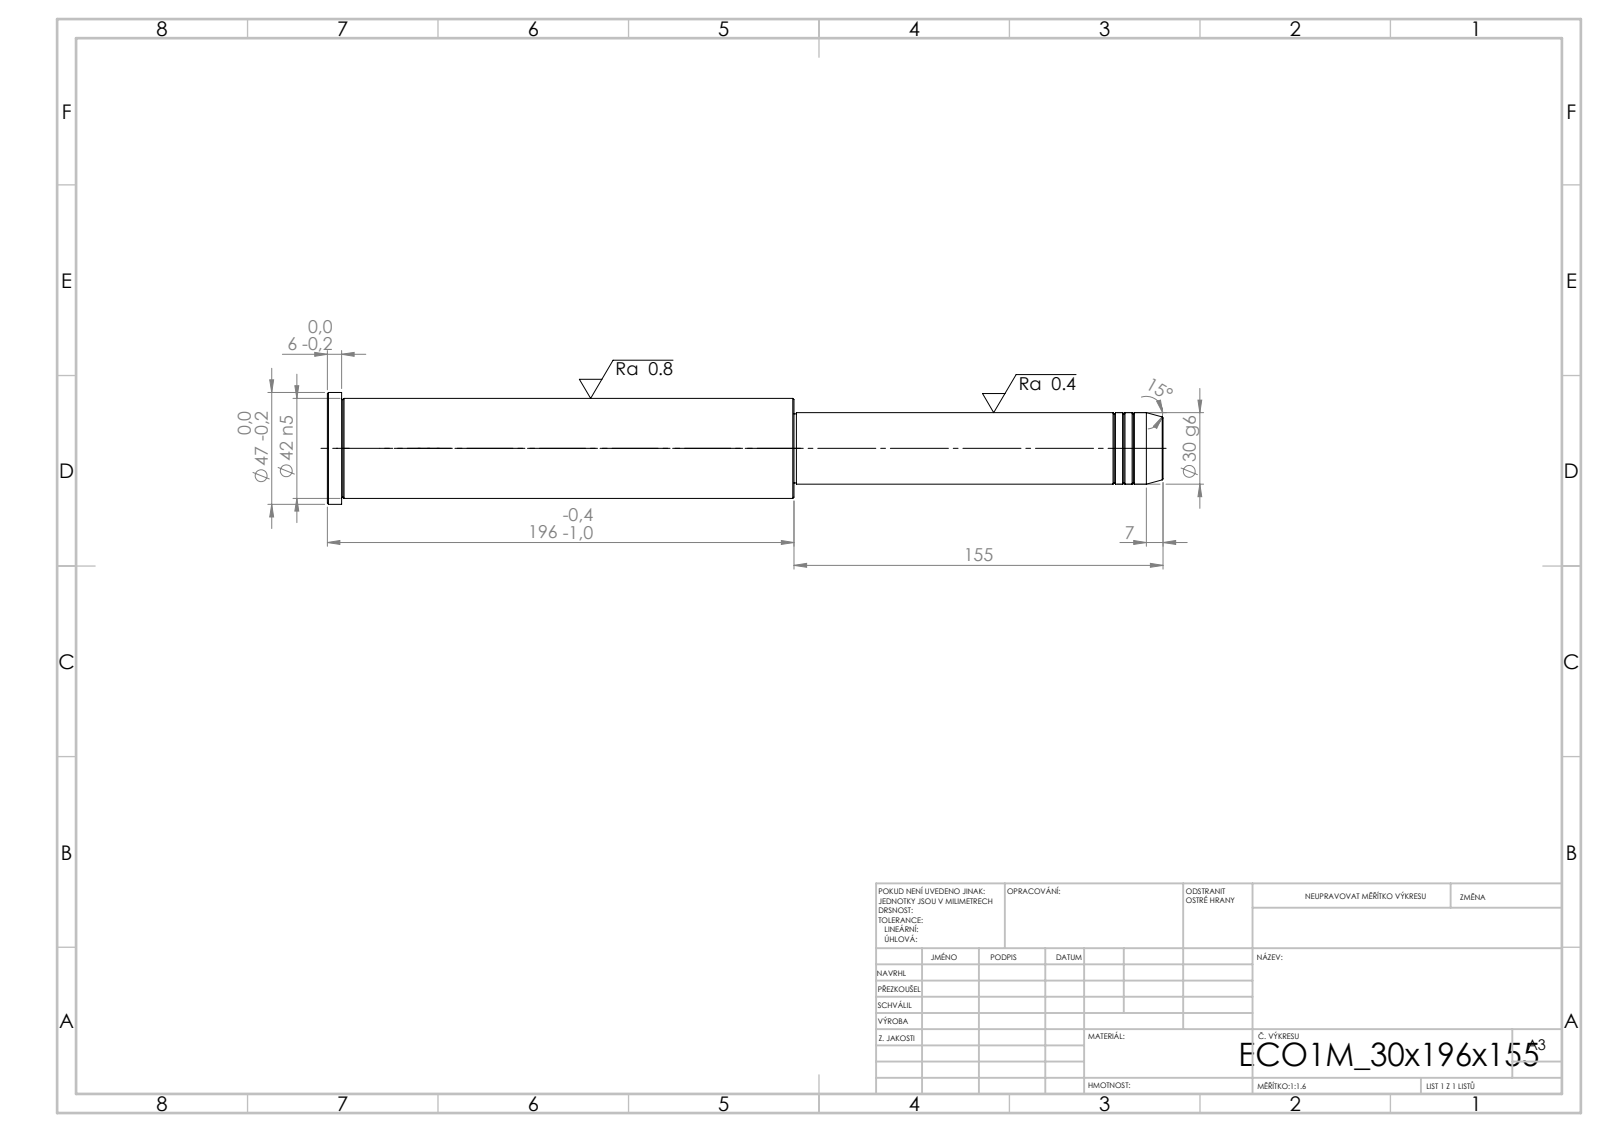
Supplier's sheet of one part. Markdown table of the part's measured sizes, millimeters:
| quantity | value |
| --- | --- |
| STEP written by | SolidWorks 2019 (CONFIG_CONTROL_DESIGN) |
| units | millimeters |
| bodies | 1 solid, 43 faces (5 planar, 14 cylindrical, 24 other) |
| overall size | 351 × 47 × 47 |
| volume | 382 370 mm³ |
| surface area | 44 071 mm² |
| round bosses / shafts (diameter × count) | 47 × 1, 42 × 1, 30 × 1, 29 × 1 |
| main face-to-face distances | 196, 155, 351, 345, 190, 6, 154, 1, 191, 197 |
